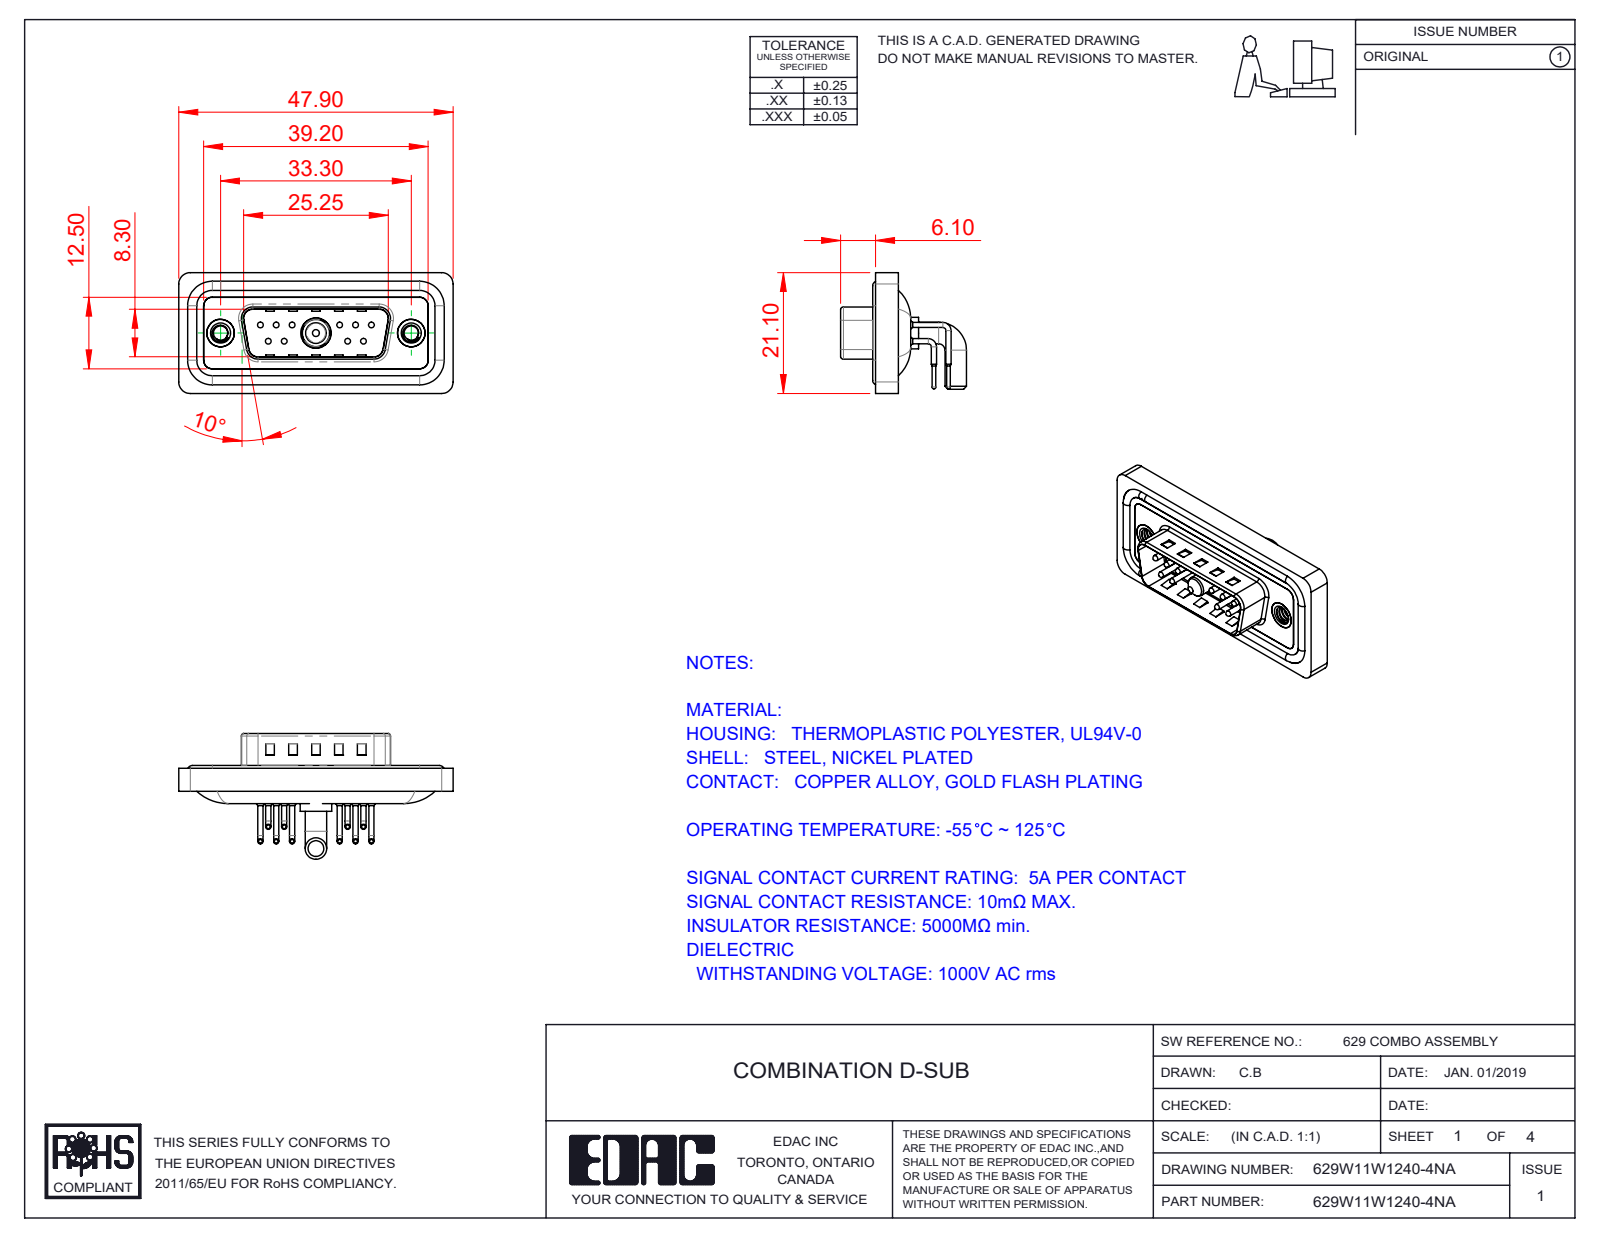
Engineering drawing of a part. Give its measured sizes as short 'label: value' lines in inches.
name: 629Combo Shell Front_15 Contacts; 629W11W1240-4NA; 629Combo Contact Row 2; Power Pin_40A RA (+5 more)
written by: SolidWorks 2020 (CONFIG_CONTROL_DESIGN)
unit: in
bodies: 19 solids, 1597 faces (836 planar, 567 cylindrical, 194 other)
size: 1.886 × 0.865 × 0.831
volume: 0.346 in³; area: 14.46 in²
holes: 10× ⌀0.03, 10× ⌀0.063, 10× ⌀0.079, 2× ⌀0.098, 2× ⌀0.157, 2× ⌀0.189, 2× ⌀0.197, 1× ⌀0.191, 1× ⌀0.209
bosses: 20× ⌀0.035, 10× ⌀0.059, 10× ⌀0.039, 10× ⌀0.026, 4× ⌀0.063, 2× ⌀0.193, 2× ⌀0.148, 1× ⌀0.217
rounds: 20× R0.079, 18× R0.059, 10× R0.04, 8× R0.02, 8× R0.063, 7× R0.039, 4× R0.01, 4× R0.024
face distances: 0.016, 0.114, 0.031, 0.043, 0.083, 0.063, 0.098, 0.161, 0.177, 0.122
hole spacings: 0.124, 0.109, 0.545, 0.436, 0.654, 0.198, 0.198, 0.218
